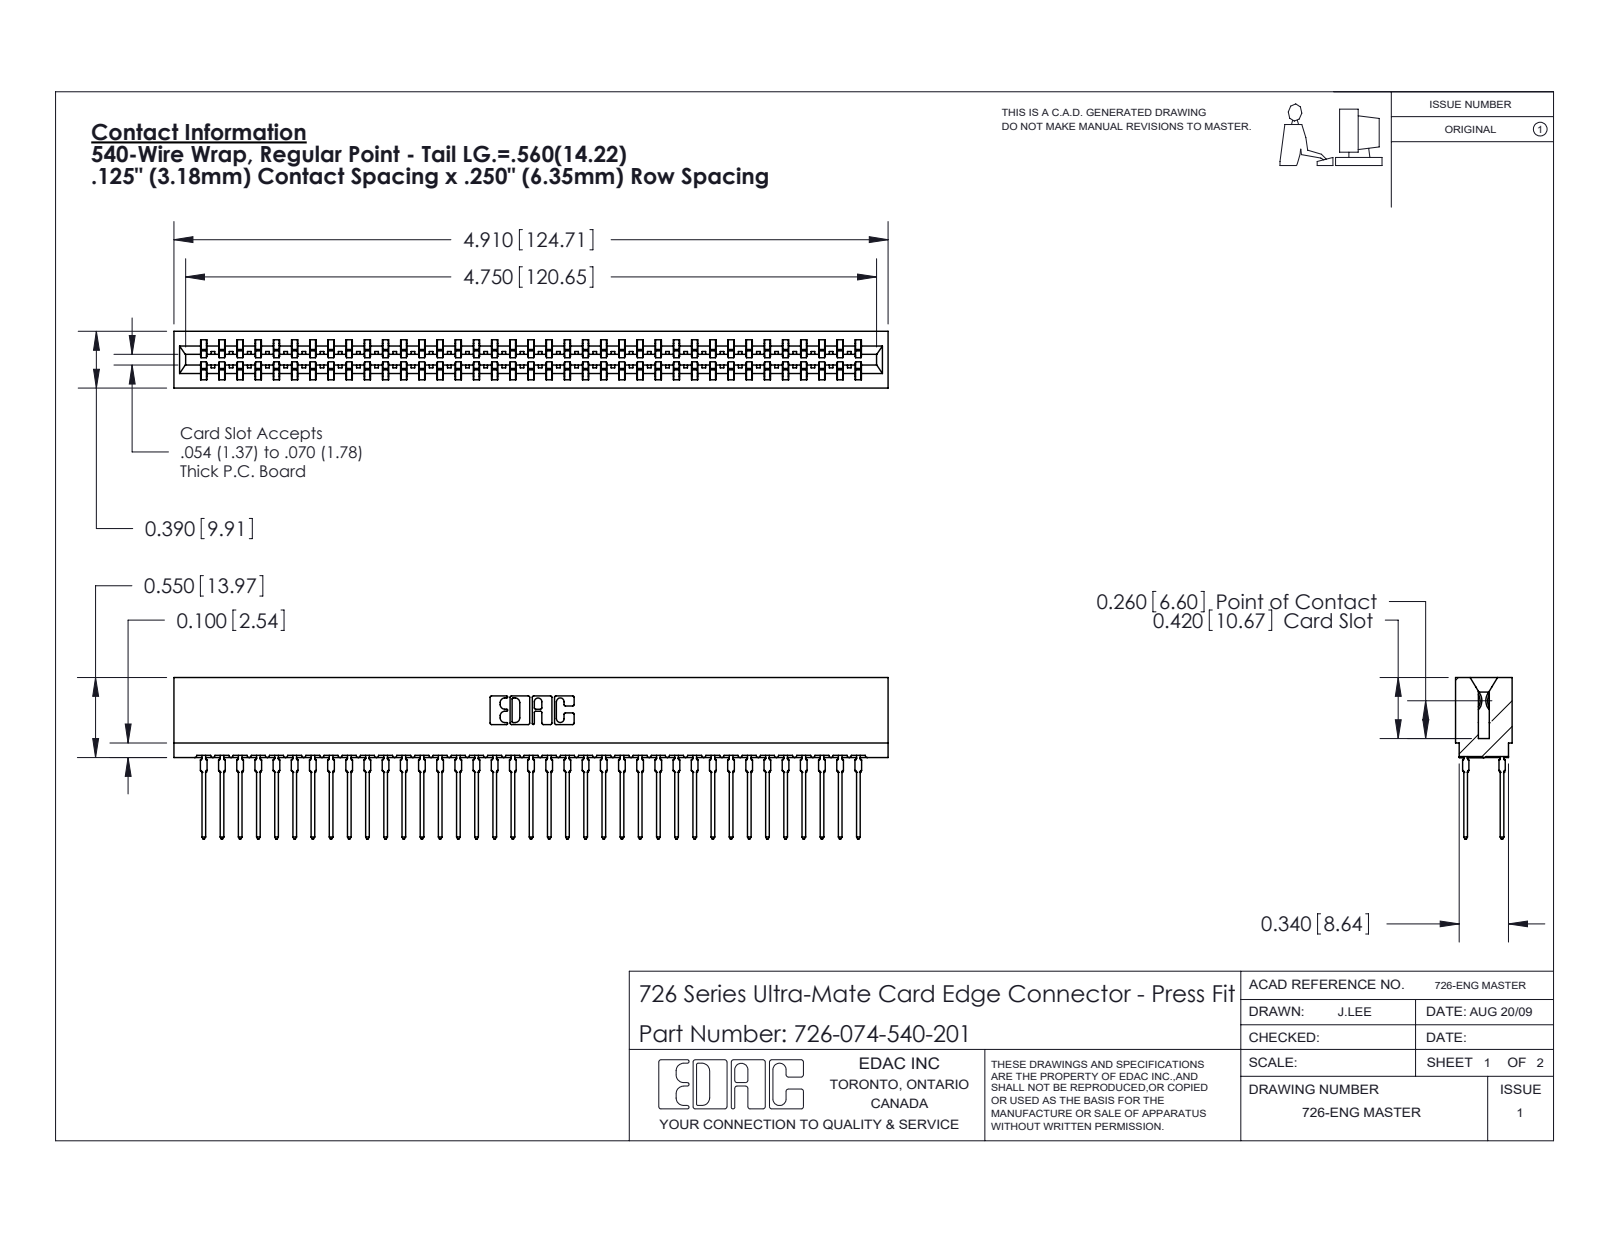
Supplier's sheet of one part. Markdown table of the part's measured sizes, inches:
| quantity | value |
| --- | --- |
| part name | 726 Part_.515 Slot Depth - 01; 726-074-540-201; 746-292-001_540 |
| STEP written by | SolidWorks 2020 (CONFIG_CONTROL_DESIGN) |
| units | inches |
| bodies | 75 solids, 6720 faces (3459 planar, 1337 cylindrical, 1924 other) |
| overall size | 4.91 × 1.109 × 0.39 |
| volume | 0.716 in³ |
| surface area | 31.77 in² |
| partial cylindrical surfaces (radius × count) | 0.021 × 148, 0.015 × 38, 0.01 × 22, 0.005 × 8, 0.011 × 8, 0.007 × 6, 0.031 × 6, 0.026 × 3 |
| main face-to-face distances | 0.057, 0.333, 0.25, 0.025, 0.307, 0.39, 0.083, 0.275, 0.5, 0.365 |
